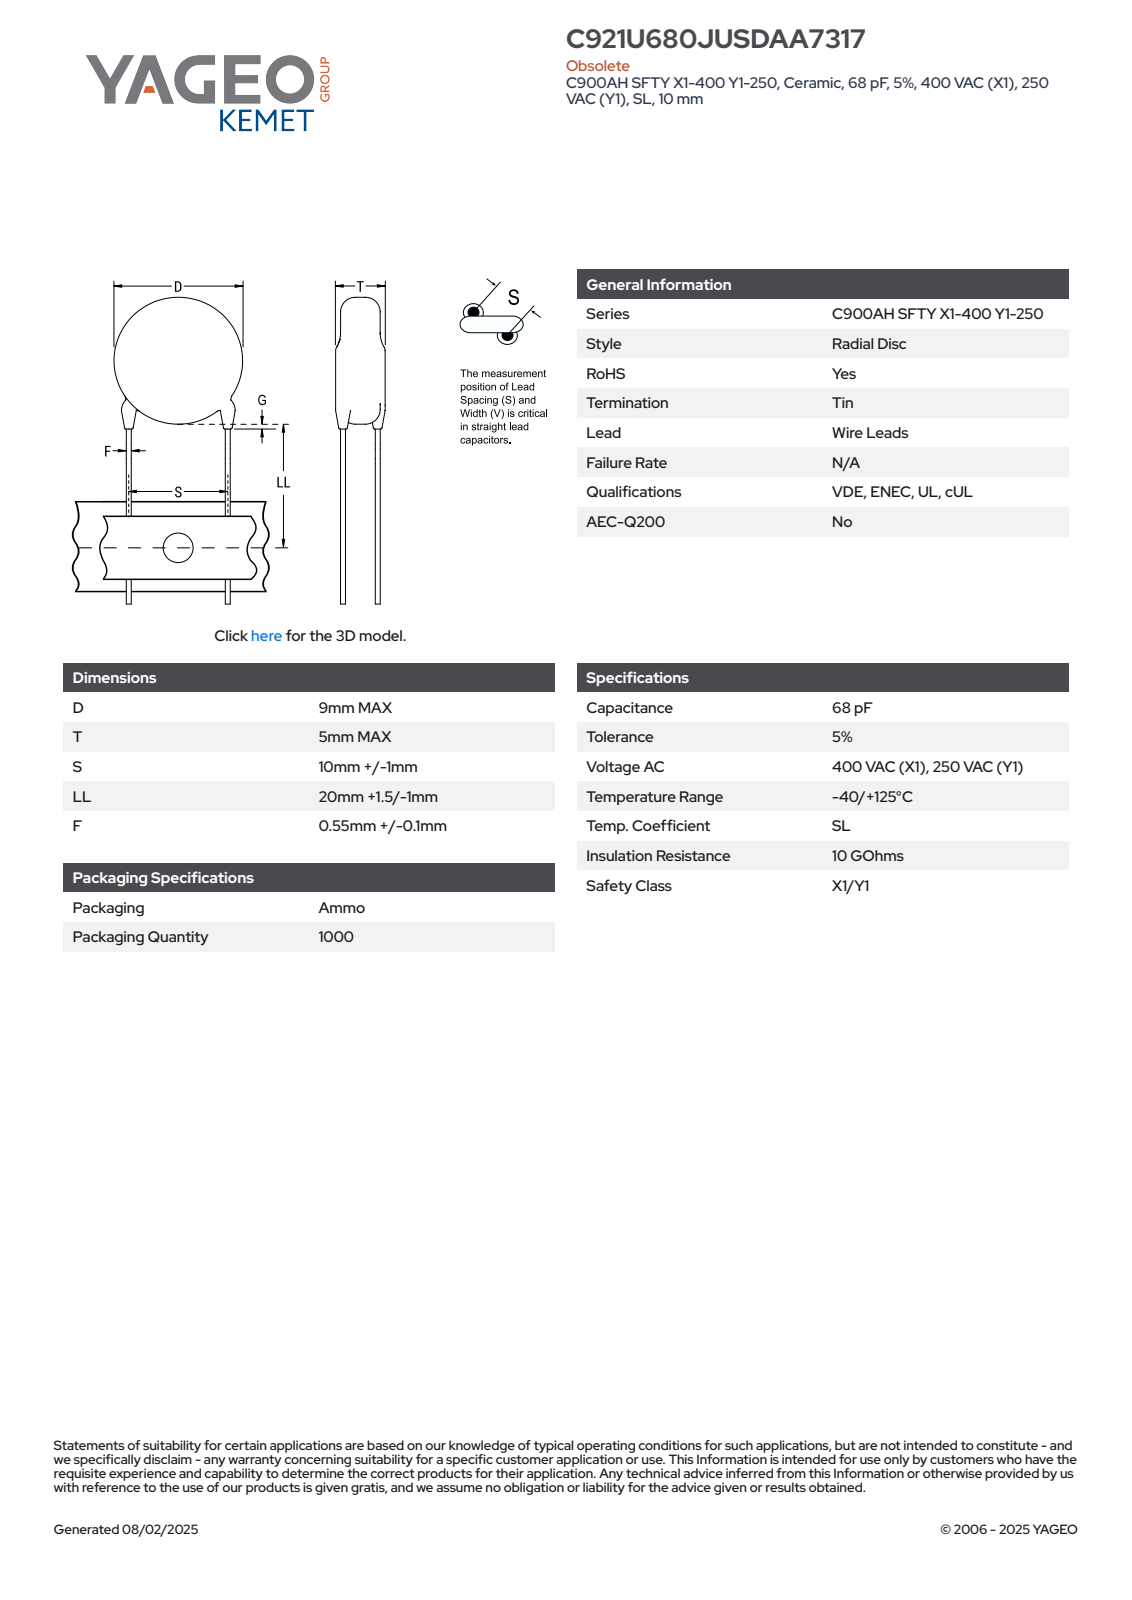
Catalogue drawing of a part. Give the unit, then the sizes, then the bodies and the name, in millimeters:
Units: millimetres
Overall size (bounding box): 30.5 × 9.69 × 5.49
Round bosses / shafts (diameter × count): ⌀0.65 ×2, ⌀9 ×1
Main face-to-face distances: 5, 1.04, 26.52, 25.48, 0.84, 0.45, 0.39, 2.14, 3.08, 3.2
Volume: 325 mm³ · Surface area: 350 mm²
Bodies: 4 solids, 83 faces (61 planar, 6 cylindrical, 16 other)
Part name (STEP PRODUCT): CCD_STC900_D9T5S10LL21.5F0.65G3
STEP written by: SolidWorks 2014 (AUTOMOTIVE_DESIGN)
